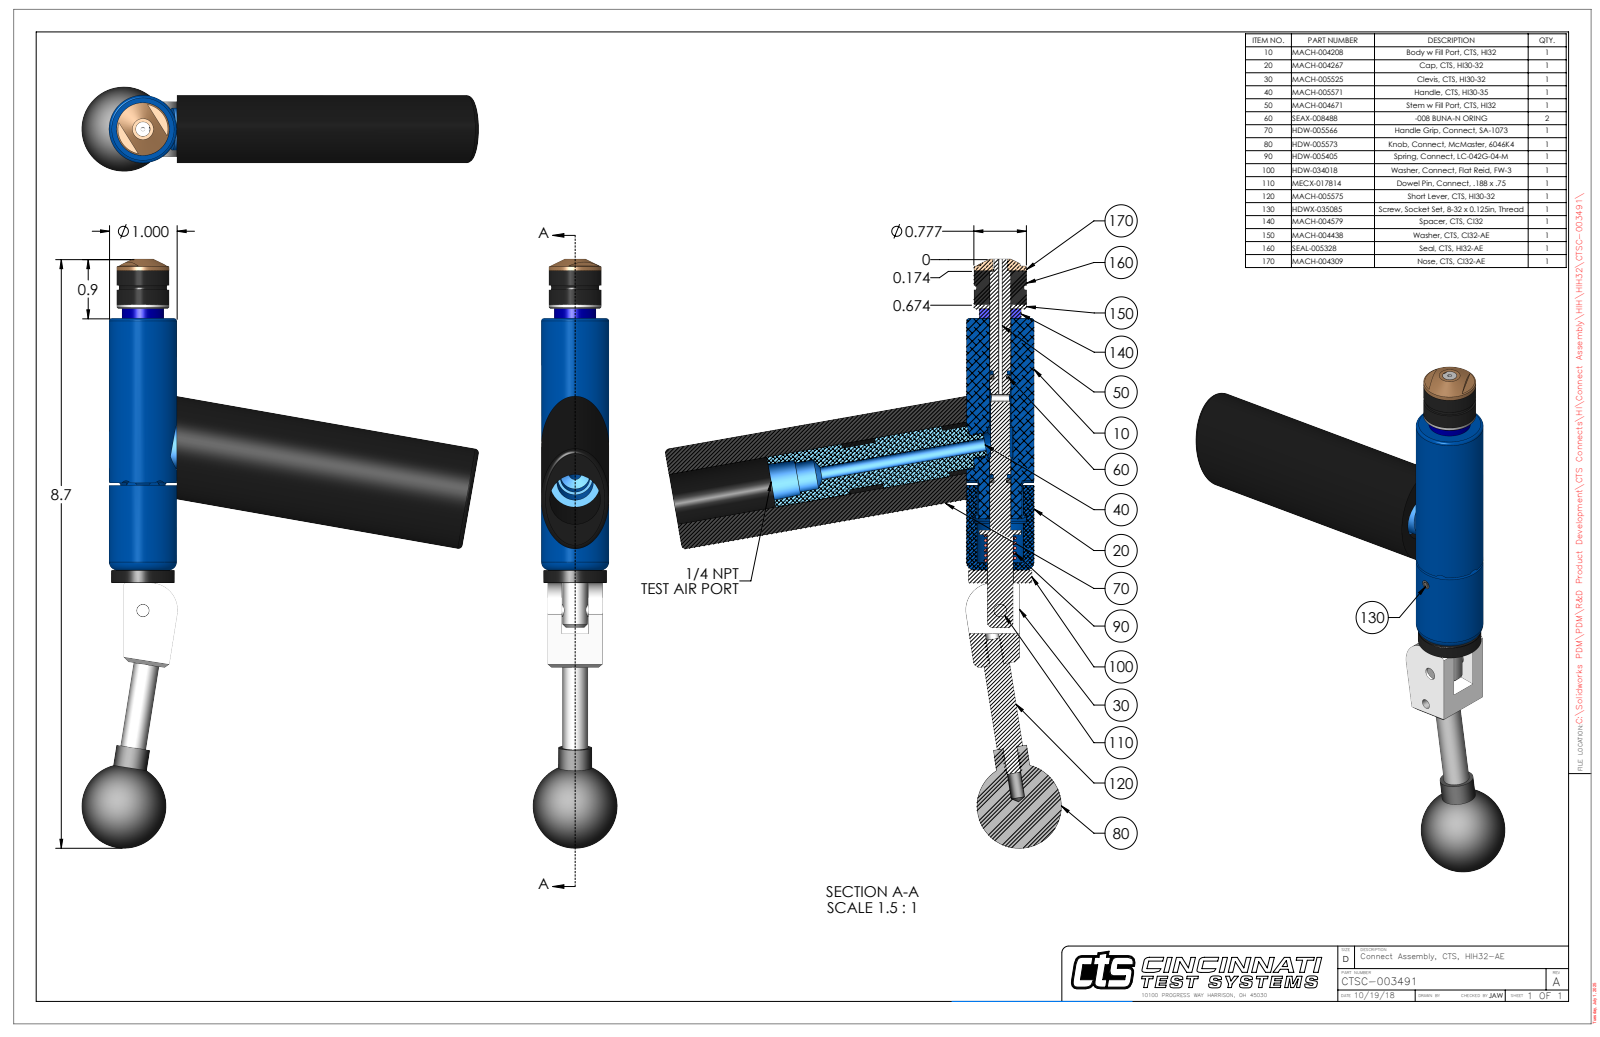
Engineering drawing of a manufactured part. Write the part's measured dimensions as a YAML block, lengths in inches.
part_name: "CTSC-003491"
step_written_by: "SolidWorks 2023 (AUTOMOTIVE_DESIGN)"
units: inches
bodies: {solids: 11, faces: 296, planar: 101, cylindrical: 127, other: 68}
overall_size: [8.704, 5.856, 1.25]
volume: 9.41
surface_area: 78.48
round_holes:
  - {diameter: 0.201, count: 2}
  - {diameter: 0.063, count: 1}
  - {diameter: 0.109, count: 1}
  - {diameter: 0.136, count: 1}
  - {diameter: 0.15, count: 1}
  - {diameter: 0.187, count: 1}
  - {diameter: 0.189, count: 1}
  - {diameter: 0.213, count: 1}
  - {diameter: 0.31, count: 1}
  - {diameter: 0.314, count: 1}
  - {diameter: 0.316, count: 1}
  - {diameter: 0.385, count: 1}
round_bosses_or_shafts:
  - {diameter: 0.25, count: 2}
  - {diameter: 0.201, count: 2}
  - {diameter: 1, count: 1}
  - {diameter: 0.936, count: 1}
  - {diameter: 0.777, count: 1}
  - {diameter: 0.75, count: 1}
  - {diameter: 0.62, count: 1}
  - {diameter: 0.618, count: 1}
partial_cylinders:
  - {radius: 0.093, count: 6}
  - {radius: 0.029, count: 2}
  - {radius: 0.069, count: 1}
  - {radius: 0.325, count: 1}
  - {radius: 0.4, count: 1}
  - {radius: 0.456, count: 1}
face_to_face_distances: [0.21, 0.602, 4.42, 0.5, 0.702, 3.719, 0.202, 3.92, 0.812, 4.608]
hole_center_spacings: [0.599, 1.658, 2.252]
